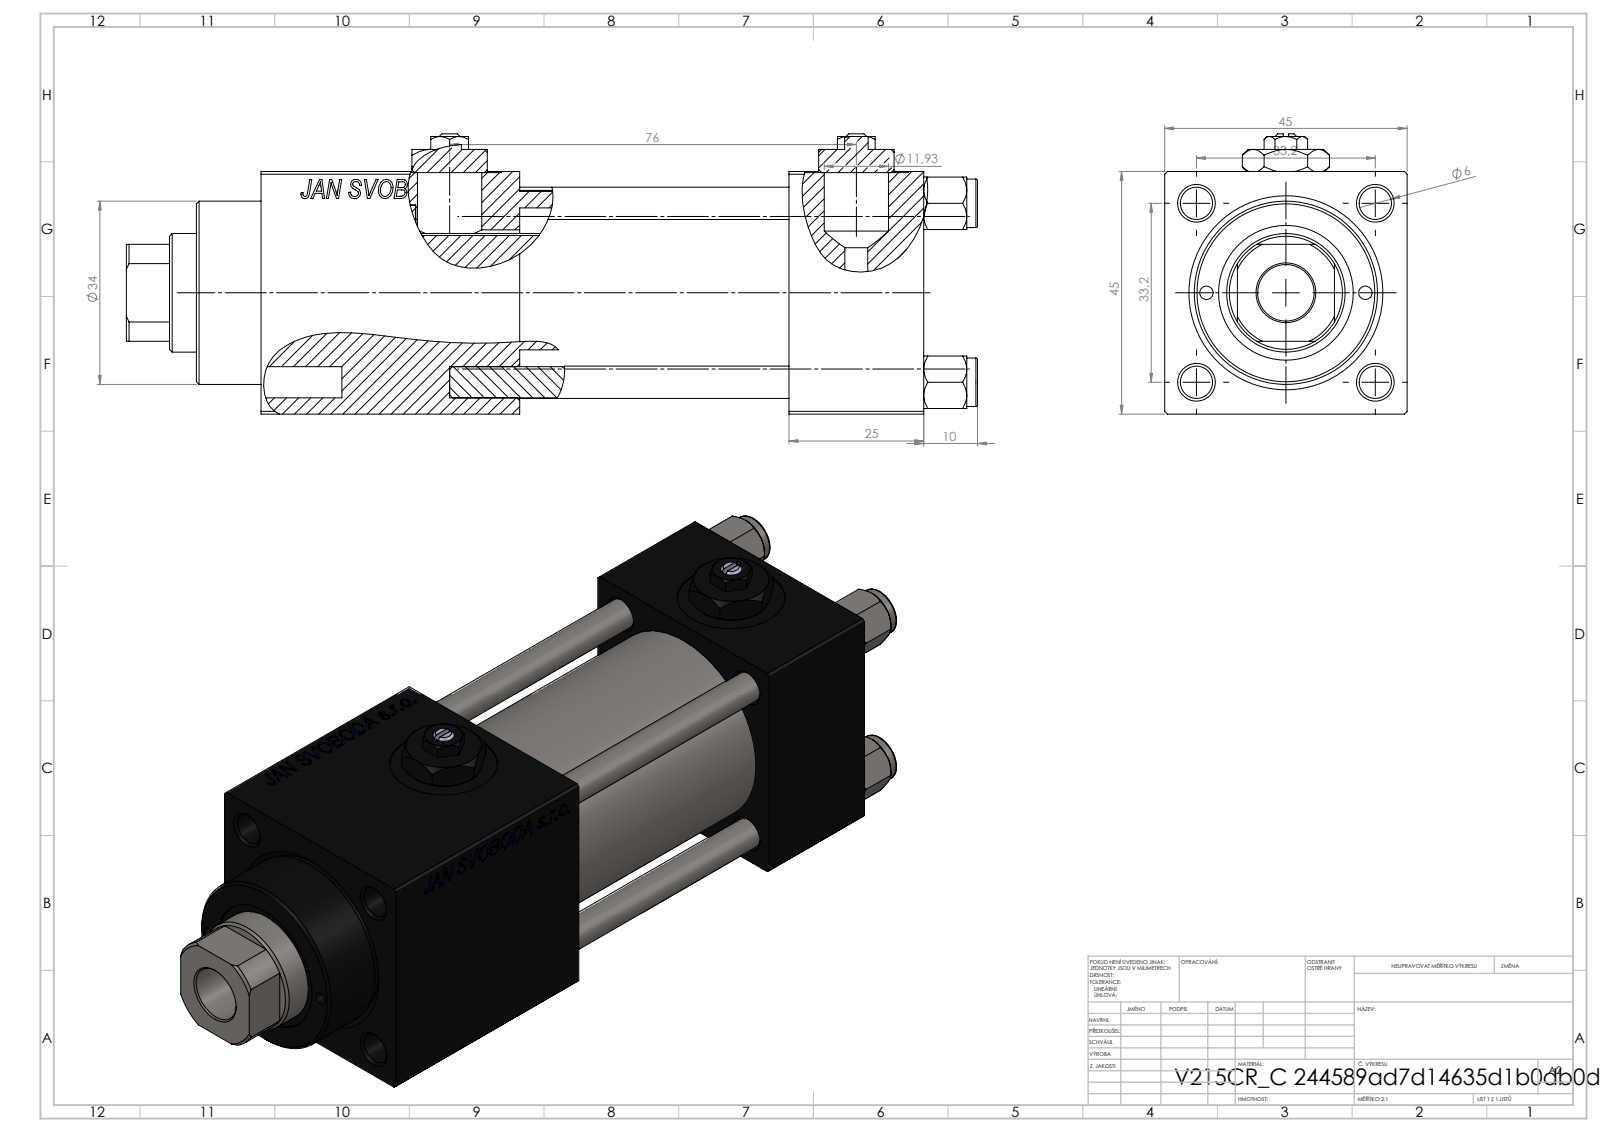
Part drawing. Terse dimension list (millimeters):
name: V215CR_C_Body; V215_VC_A; NUT_M5_C; V215CR_VCP_C (+2 more)
written by: SolidWorks 2019 (CONFIG_CONTROL_DESIGN)
unit: mm
bodies: 13 solids, 1254 faces (574 planar, 102 cylindrical, 578 other)
size: 158 × 52 × 45
volume: 207 736 mm³; area: 73 475 mm²
holes: 4× ⌀6, 2× ⌀2.5, 2× ⌀7, 2× ⌀13.16, 2× ⌀20, 1× ⌀10.5, 1× ⌀22, 1× ⌀24, 1× ⌀25, 1× ⌀32, 1× ⌀33
bosses: 4× ⌀9, 1× ⌀38, 1× ⌀34
rounds: 1× R10.5
face distances: 45, 25, 50, 123, 75, 98, 44.8, 48, 94.3, 69.3
hole spacings: 16.7, 23.48, 33.2, 35.47, 14.75, 46.95, 29.5, 75.5
